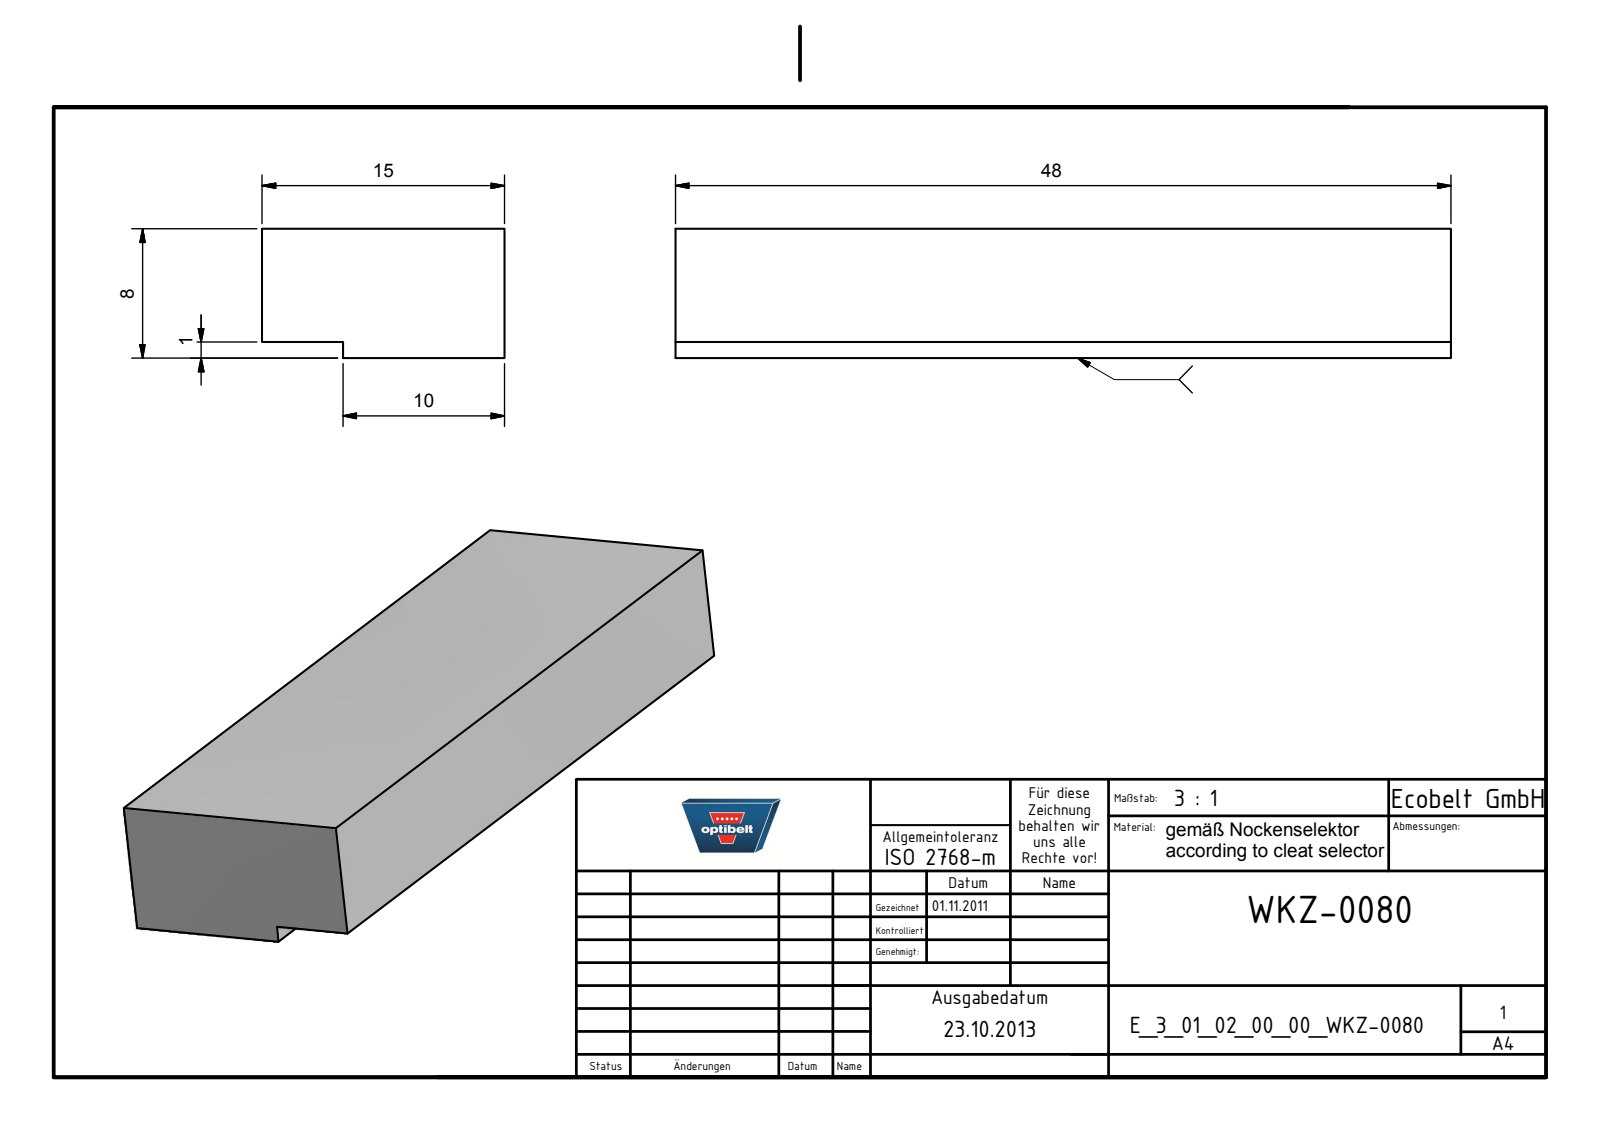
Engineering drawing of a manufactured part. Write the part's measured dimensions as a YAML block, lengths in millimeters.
part_name: "E_3_01_04_16_00_WKZ-0080"
step_written_by: "Autodesk Inventor 2025 (AUTOMOTIVE_DESIGN)"
units: millimeters
bodies: {solids: 1, faces: 8, planar: 8, cylindrical: 0, other: 0}
overall_size: [48, 15, 8]
volume: 5520
surface_area: 2438
face_to_face_distances: [8, 15, 1, 7, 48, 5, 10]
